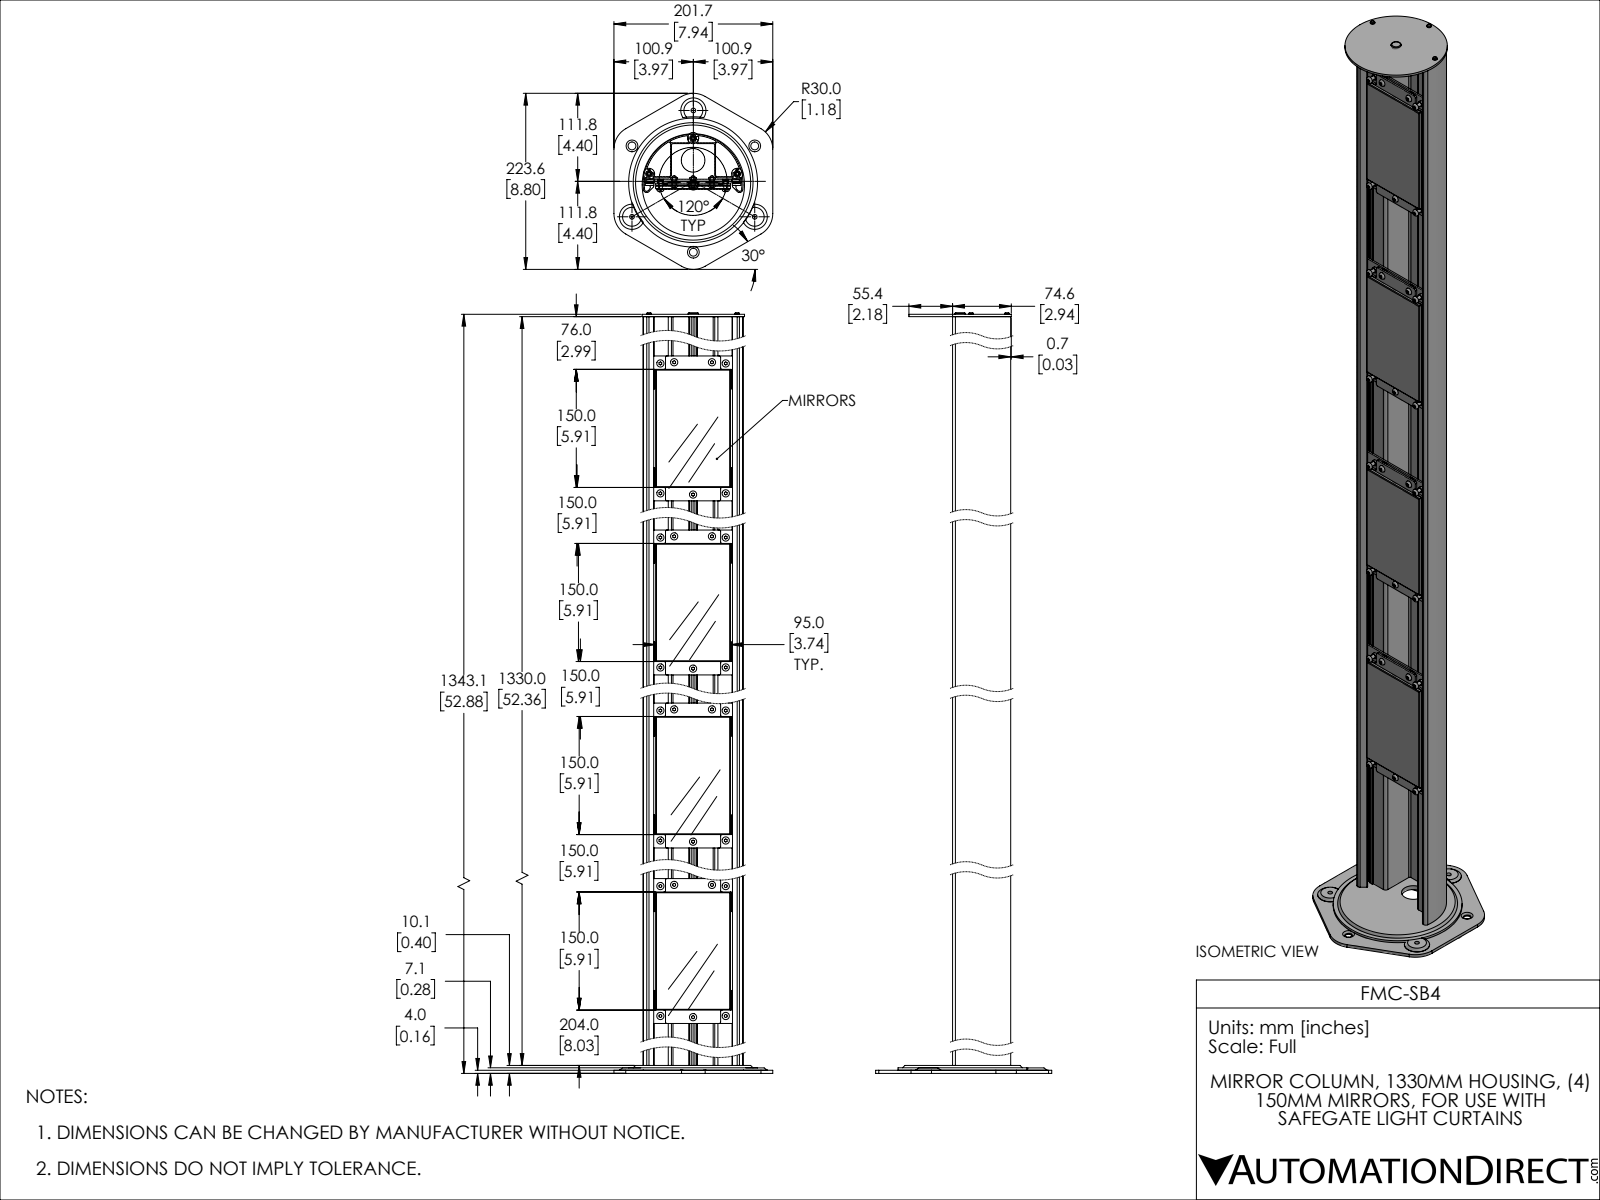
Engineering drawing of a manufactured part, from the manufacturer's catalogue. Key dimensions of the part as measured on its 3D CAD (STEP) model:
Part name (STEP PRODUCT): FMC-SB4
STEP written by: SolidWorks 2019 (AUTOMOTIVE_DESIGN)
Units: inches
Bodies: 107 solids, 1414 faces (823 planar, 473 cylindrical, 118 other)
Overall size (bounding box): 52.959 × 8.805 × 7.942
Volume: 125 in³ · Surface area: 2 993 in²
Round holes (diameter × count): ⌀0.197 ×16, ⌀0.287 ×16, ⌀0.189 ×12, ⌀0.209 ×12, ⌀0.217 ×12, ⌀0.256 ×12, ⌀0.157 ×3, ⌀0.236 ×3, ⌀0.335 ×3, ⌀0.394 ×3, ⌀1.181 ×1, ⌀3.406 ×1
Round bosses / shafts (diameter × count): ⌀0.28 ×16, ⌀0.343 ×12, ⌀0.251 ×12, ⌀0.197 ×12, ⌀0.248 ×3, ⌀0.227 ×3, ⌀0.138 ×3, ⌀6.445 ×1
Partial cylindrical surfaces — rounded edges, fillets, slot ends (radius × count): R0.02 ×58, R0.039 ×39, R0.079 ×37, R0.098 ×32, R1.181 ×6, R0.217 ×4, R0.106 ×3, R0.63 ×3
Main face-to-face distances: 0.098, 0.197, 0.296, 0.099, 0.31, 0.211, 0.113, 0.014, 0.507, 0.408
Hole centre spacings: 11.811, 23.622, 12.255, 0.691, 1.635, 2.58, 3.268, 3.543
